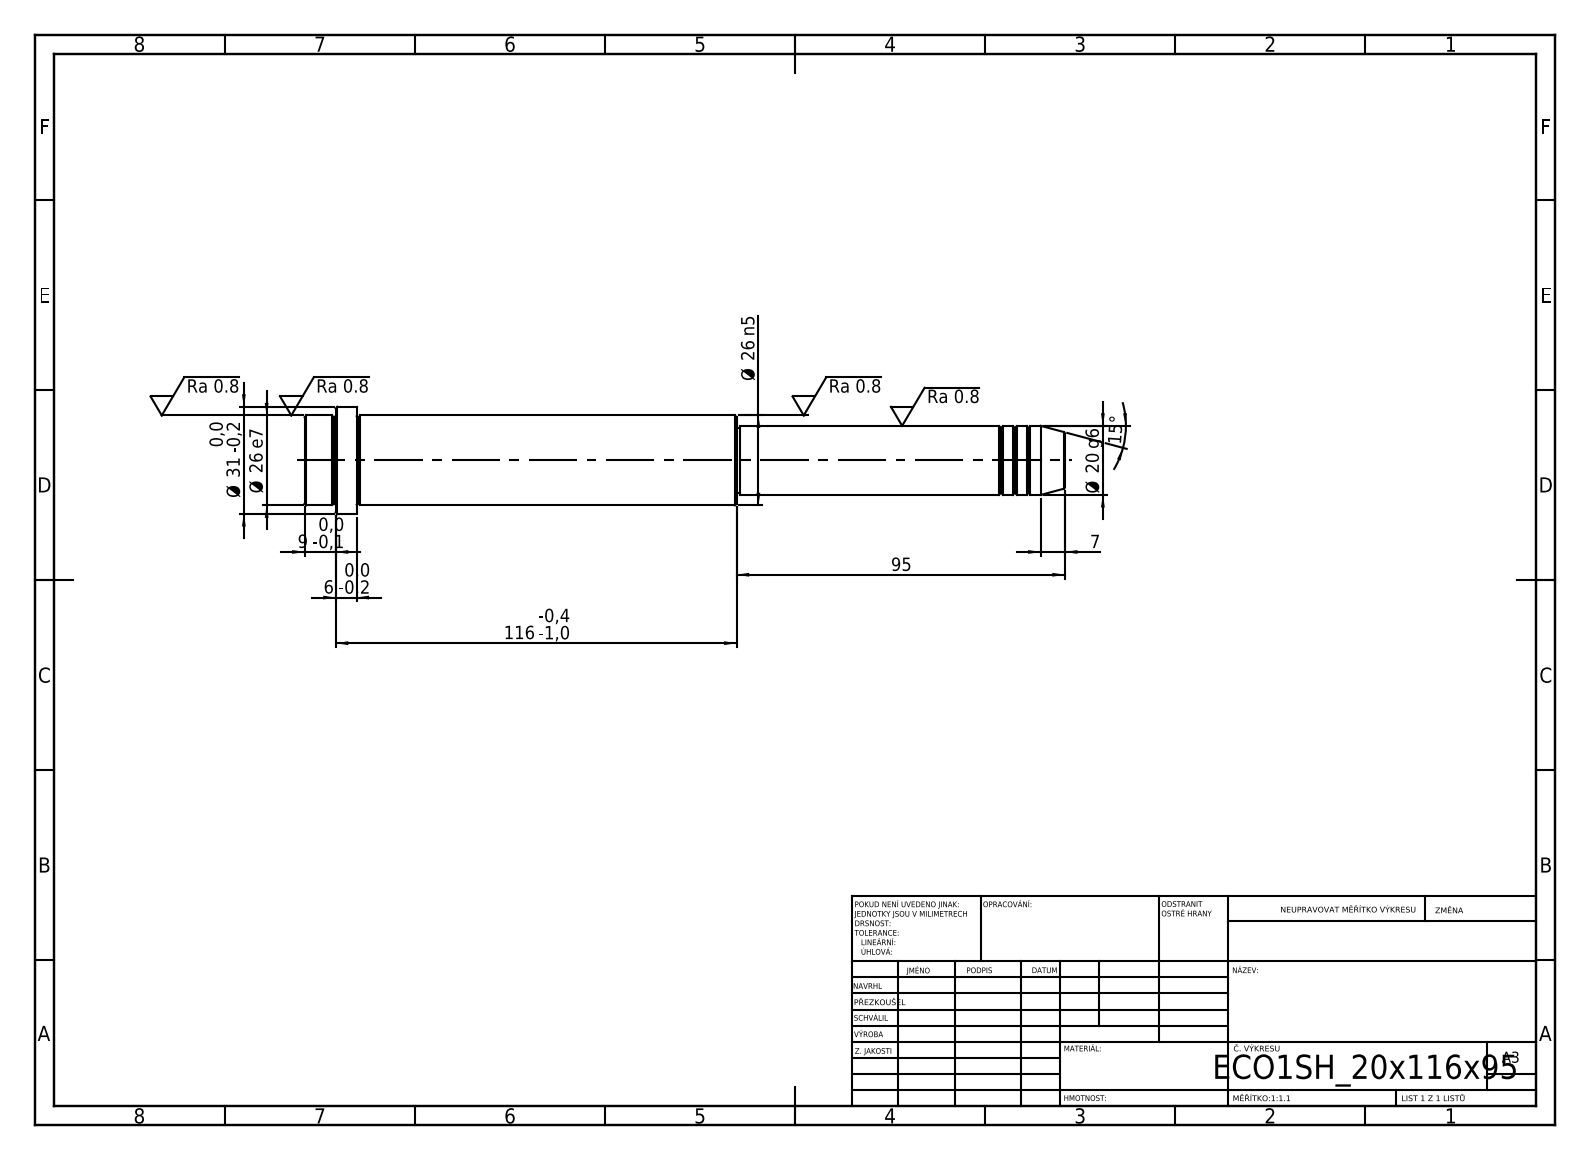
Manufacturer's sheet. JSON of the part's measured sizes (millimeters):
{"step_written_by": "SolidWorks 2019 (CONFIG_CONTROL_DESIGN)", "units": "millimeters", "bodies": {"solids": 1, "faces": 52, "planar": 6, "cylindrical": 16, "other": 30}, "overall_size": [220, 31, 31], "volume_mm3": 96968, "surface_area_mm2": 17809, "round_bosses_or_shafts": [[31, 1], [26, 1], [20, 1], [19, 1]], "face_to_face_distances": [15, 110, 125, 95, 205, 220, 211, 116, 6, 9]}
